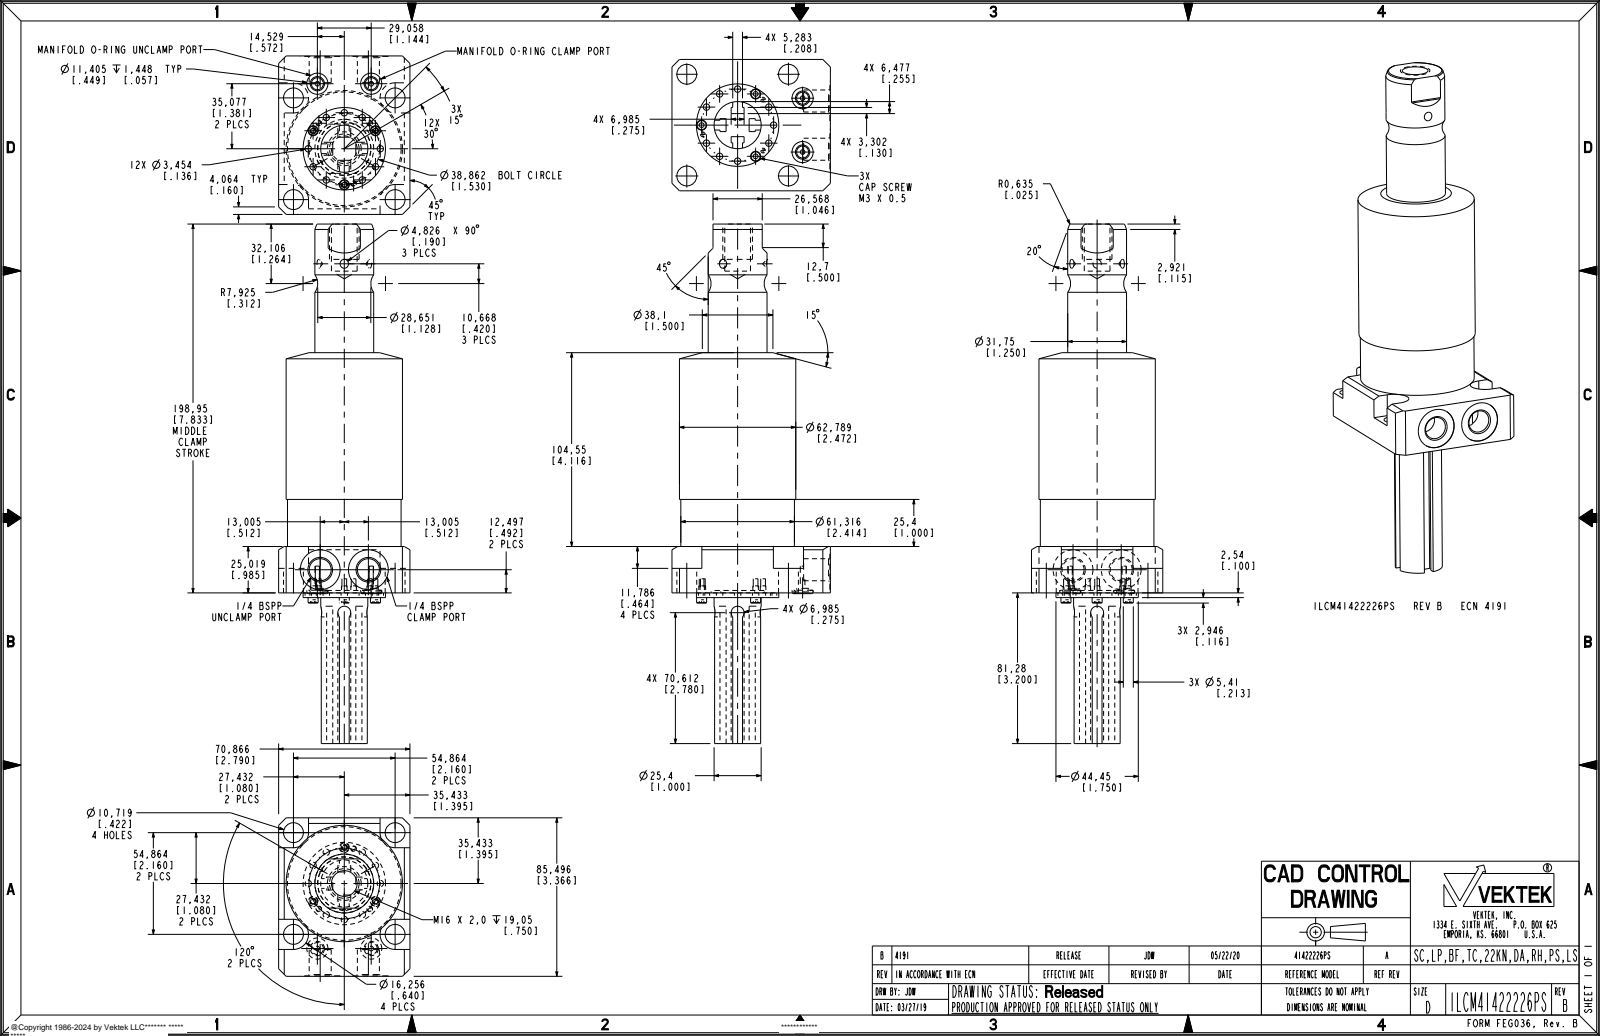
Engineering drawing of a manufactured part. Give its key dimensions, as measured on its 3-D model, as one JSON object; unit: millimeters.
{"part_name": "ILCM41422226PS", "step_written_by": "PRO/ENGINEER BY PARAMETRIC TECHNOLOGY CORPORATION, 2013320 (AUTOMOTIVE_DESIGN)", "units": "millimeters", "bodies": {"solids": 1, "faces": 282, "planar": 134, "cylindrical": 114, "other": 34}, "overall_size": [280.23, 85.5, 70.87], "volume_mm3": 527716, "surface_area_mm2": 65233, "round_holes": [[3.45, 12], [2.54, 6], [10.72, 4], [2.49, 2], [6.5, 2], [11.4, 2], [11.89, 2], [21.49, 2], [13.87, 1], [28.7, 1]], "round_bosses_or_shafts": [[3, 6], [5.41, 3], [62.79, 1], [61.32, 1], [44.45, 1], [31.75, 1], [25.4, 1], [18.26, 1]], "partial_cylinders_radius": [[8.13, 4], [0.76, 2], [3.49, 2]], "face_to_face_distances": [2.73, 9.71, 25.02, 3.58, 8.86, 0.85, 6.13, 41.65, 29.21, 70.86], "hole_center_spacings": [19.43, 33.66, 10.06, 19.44, 37.54, 20.64, 27.49, 28.57]}
